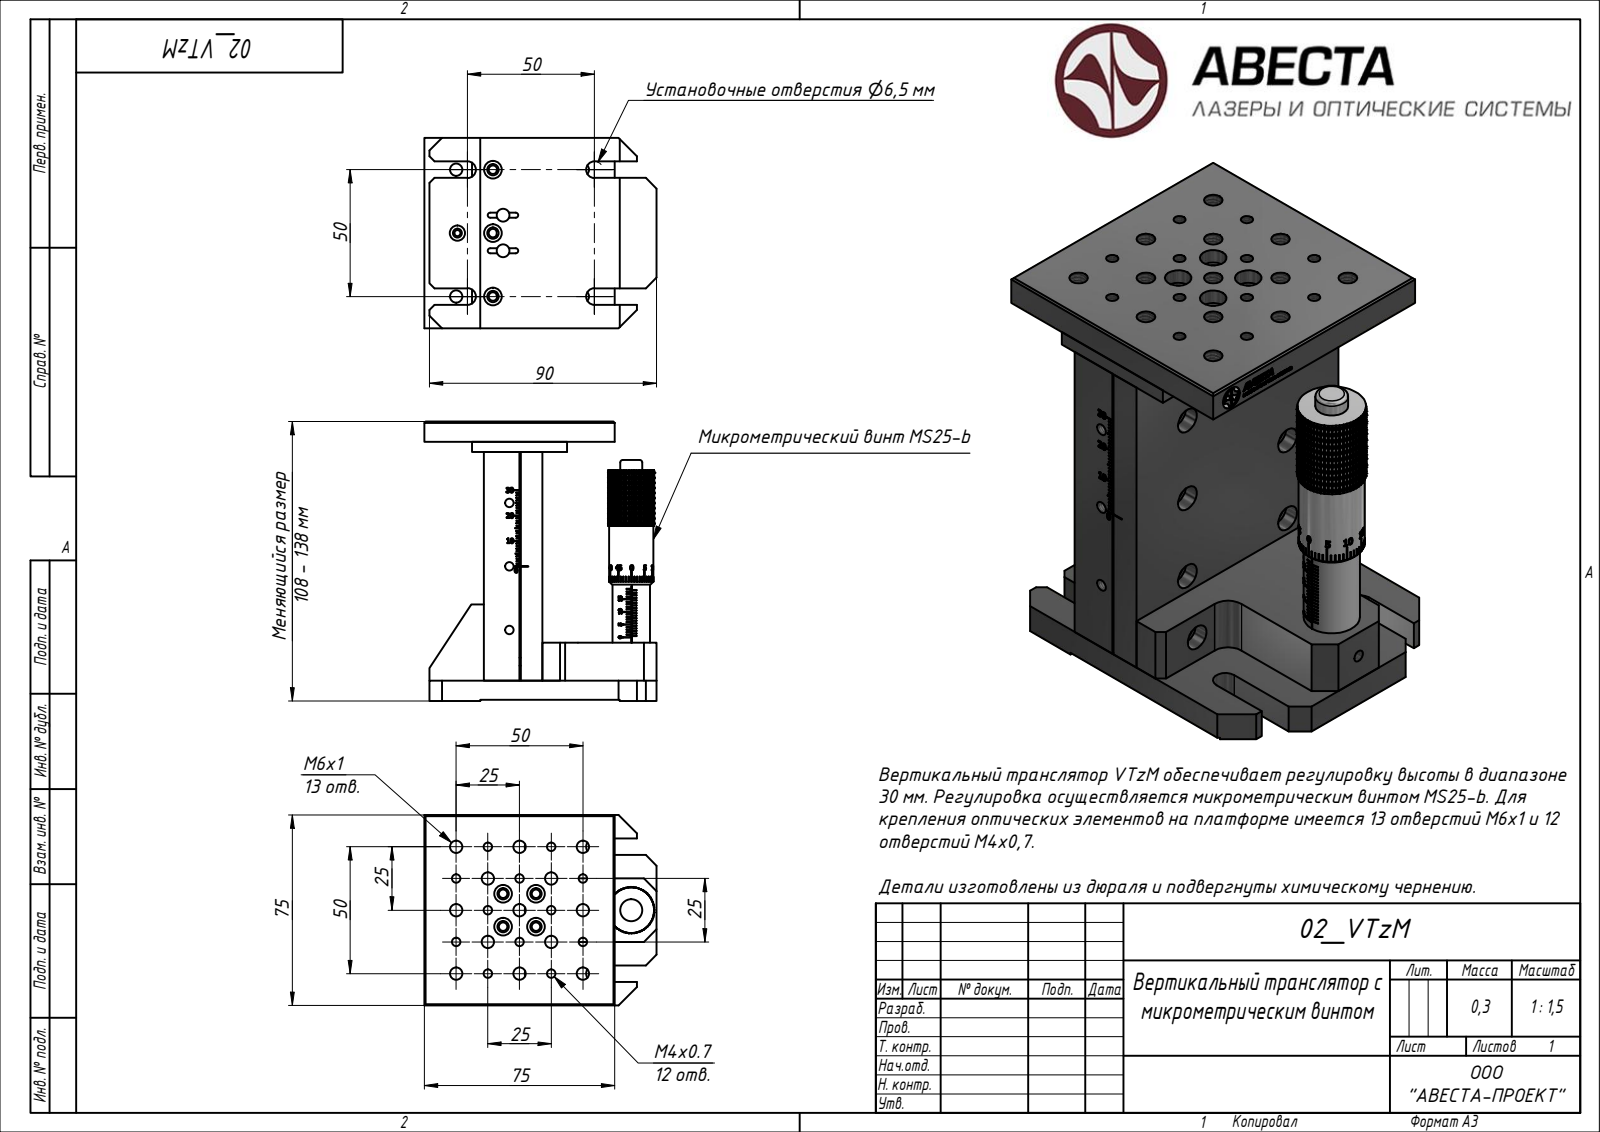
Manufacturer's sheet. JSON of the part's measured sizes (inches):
{"part_name": "02_VTzM; VTzM - Стенка платформы; P01 _ Направляющие рельсы 8х8; Рельса 8х8 (+8 more)", "step_written_by": "Autodesk Inventor 2020 (CONFIG_CONTROL_DESIGN)", "units": "inches", "bodies": {"solids": 635, "faces": 6700, "planar": 5756, "cylindrical": 337, "other": 607}, "overall_size": [4.331, 3.602, 2.953], "volume_in3": 16.51, "surface_area_in2": 173, "round_holes": [[0.128, 37], [0.177, 21], [0.276, 21], [0.236, 19], [0.194, 13], [0.097, 10], [0.138, 10], [0.217, 3], [0.062, 2], [0.197, 2], [0.256, 1], [0.315, 1]], "round_bosses_or_shafts": [[0.709, 1], [0.685, 1], [0.583, 1], [0.341, 1]], "partial_cylinders_radius": [[0.039, 4], [0.128, 4], [0.197, 2], [0.291, 1], [0.339, 1]], "face_to_face_distances": [0.315, 0.906, 0.197, 0.354, 3.701, 4.016, 0.669, 0.709, 0.157, 0.472], "hole_center_spacings": [0.984, 1.1, 0.492, 1.556, 0.696, 1.774, 1.969, 1.392]}
